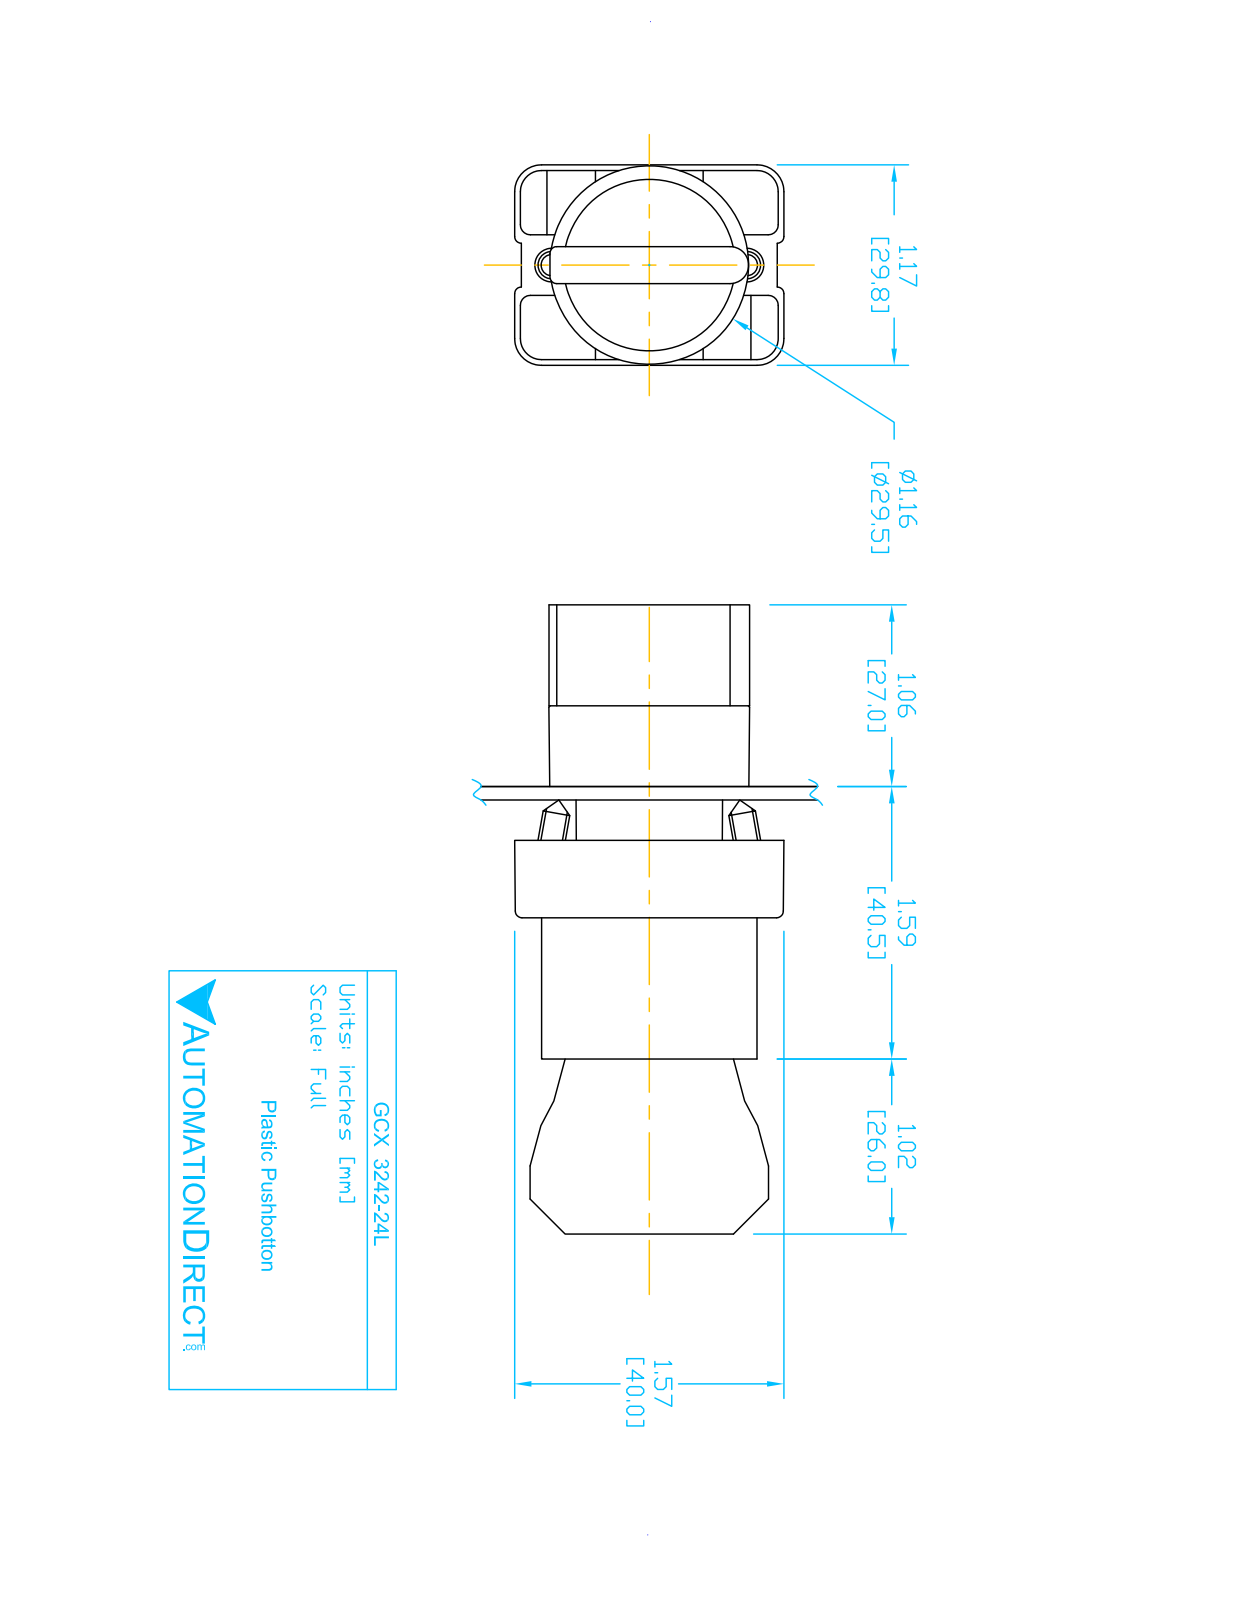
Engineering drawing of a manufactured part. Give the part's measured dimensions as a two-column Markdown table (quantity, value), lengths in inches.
| quantity | value |
| --- | --- |
| part name | GCX3242L OPERATOR; ECX1050; GCX3242-24L; ecx1040 (+1 more) |
| STEP written by | SolidWorks 2016 (AUTOMOTIVE_DESIGN) |
| units | inches |
| bodies | 8 solids, 445 faces (263 planar, 151 cylindrical, 31 other) |
| overall size | 3.653 × 1.581 × 1.177 |
| volume | 2.799 in³ |
| surface area | 39 in² |
| round holes (diameter × count) | 0.079 × 2, 0.124 × 2, 0.13 × 2, 0.087 × 1, 0.197 × 1, 0.469 × 1, 0.878 × 1, 0.888 × 1, 1.024 × 1 |
| round bosses / shafts (diameter × count) | 0.157 × 4, 1.175 × 1, 1.004 × 1, 0.945 × 1, 0.856 × 1, 0.78 × 1, 0.504 × 1 |
| partial cylindrical surfaces (radius × count) | 0.059 × 24, 0.041 × 12, 0.124 × 12, 0.157 × 12, 0.039 × 9, 0.128 × 2, 0.02 × 1, 0.063 × 1 |
| main face-to-face distances | 0.827, 2.02, 1.193, 0.579, 1.244, 1.171, 0.472, 0.469, 0.031, 0.033 |
| hole center spacings | 0.236, 0.544, 0.472, 0.49 |
